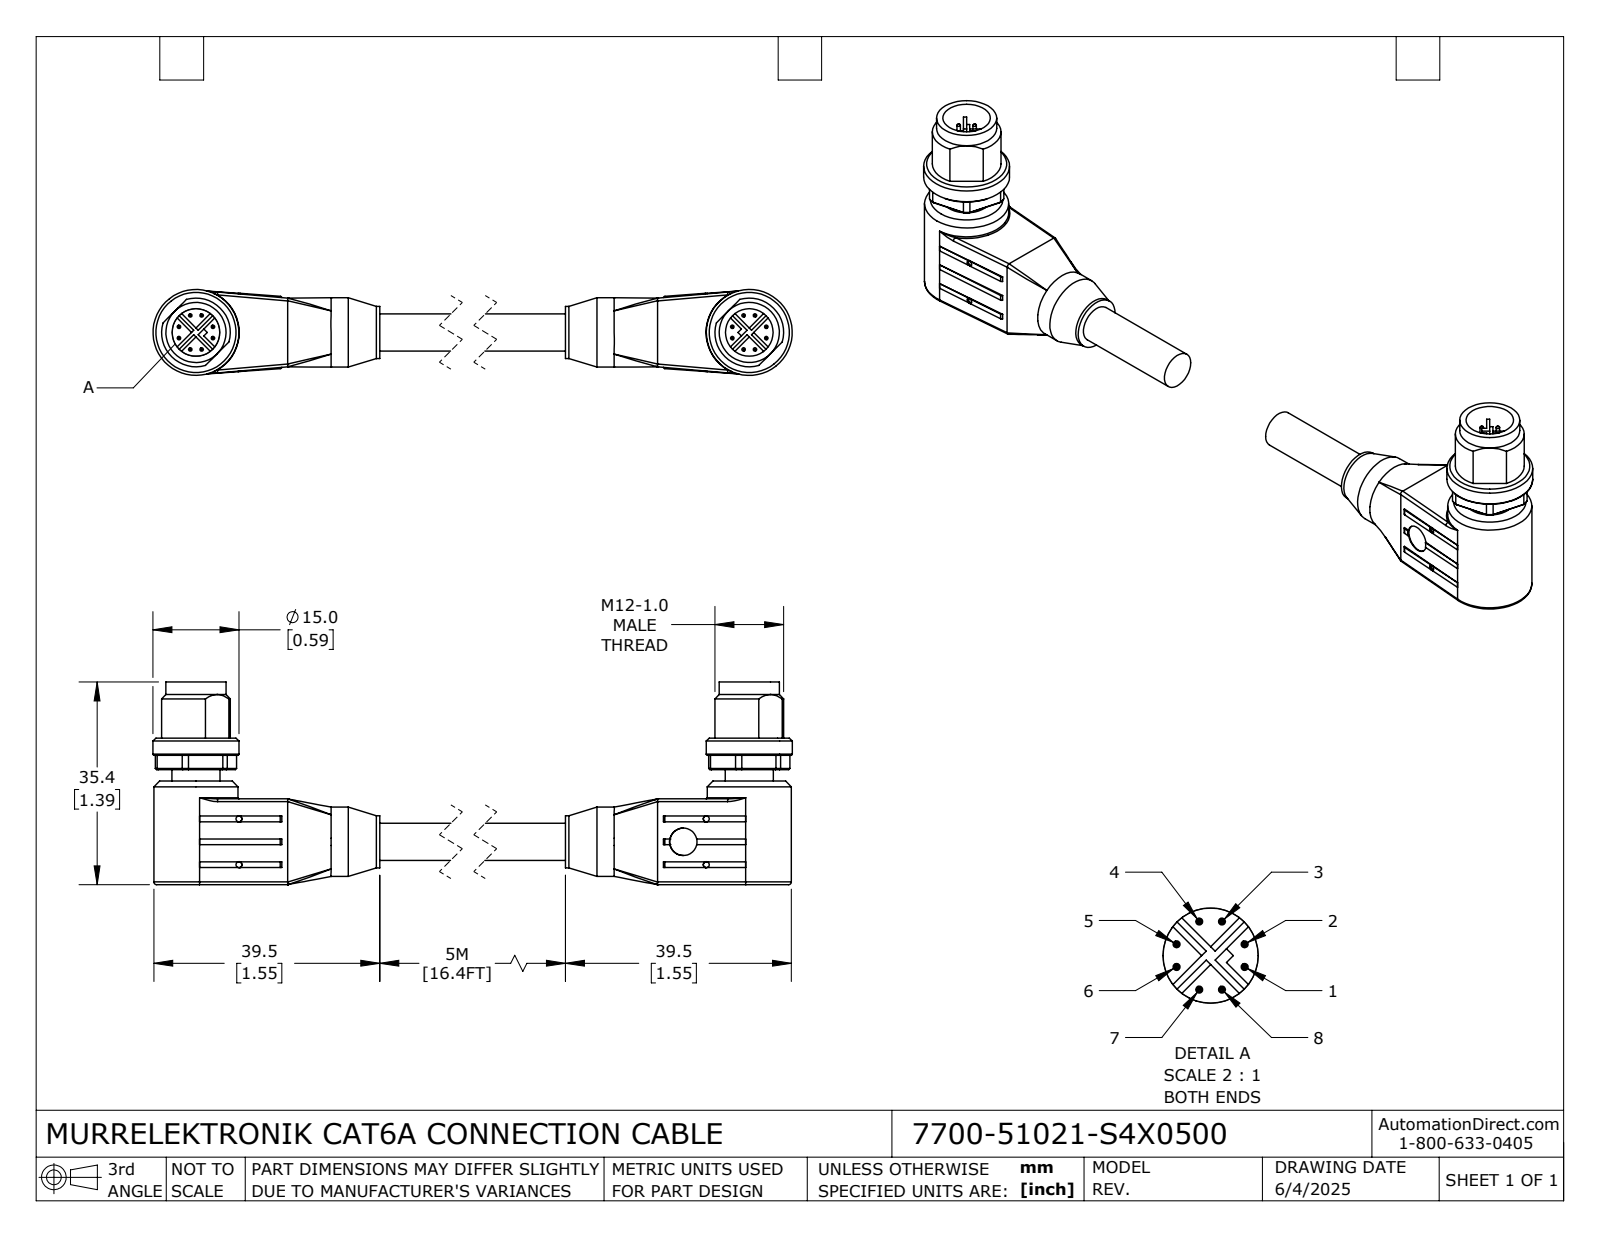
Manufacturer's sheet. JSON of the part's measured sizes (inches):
{"part_name": "7700-51021-S4X0500_MALE; 7700-51021-S4X0500", "step_written_by": "SolidWorks 2024 (CONFIG_CONTROL_DESIGN)", "units": "inches", "bodies": {"solids": 2, "faces": 424, "planar": 196, "cylindrical": 134, "other": 94}, "overall_size": [5.677, 1.394, 0.591], "volume_in3": 1.124, "surface_area_in2": 12.42, "round_holes": [[0.041, 8], [0.189, 2], [0.327, 2]], "round_bosses_or_shafts": [[0.024, 16], [0.591, 2], [0.579, 2], [0.413, 2], [0.331, 2], [0.476, 1], [0.358, 1], [0.256, 1]], "partial_cylinders_radius": [[0.02, 8], [0.012, 4], [0.236, 2], [0.283, 2]], "face_to_face_distances": [0.141, 0.591, 3.596, 0.791, 0.201, 0.713, 0.122, 0.079, 0.043, 0.185], "hole_center_spacings": [0.315, 4.521, 4.532, 4.208, 5.087]}
